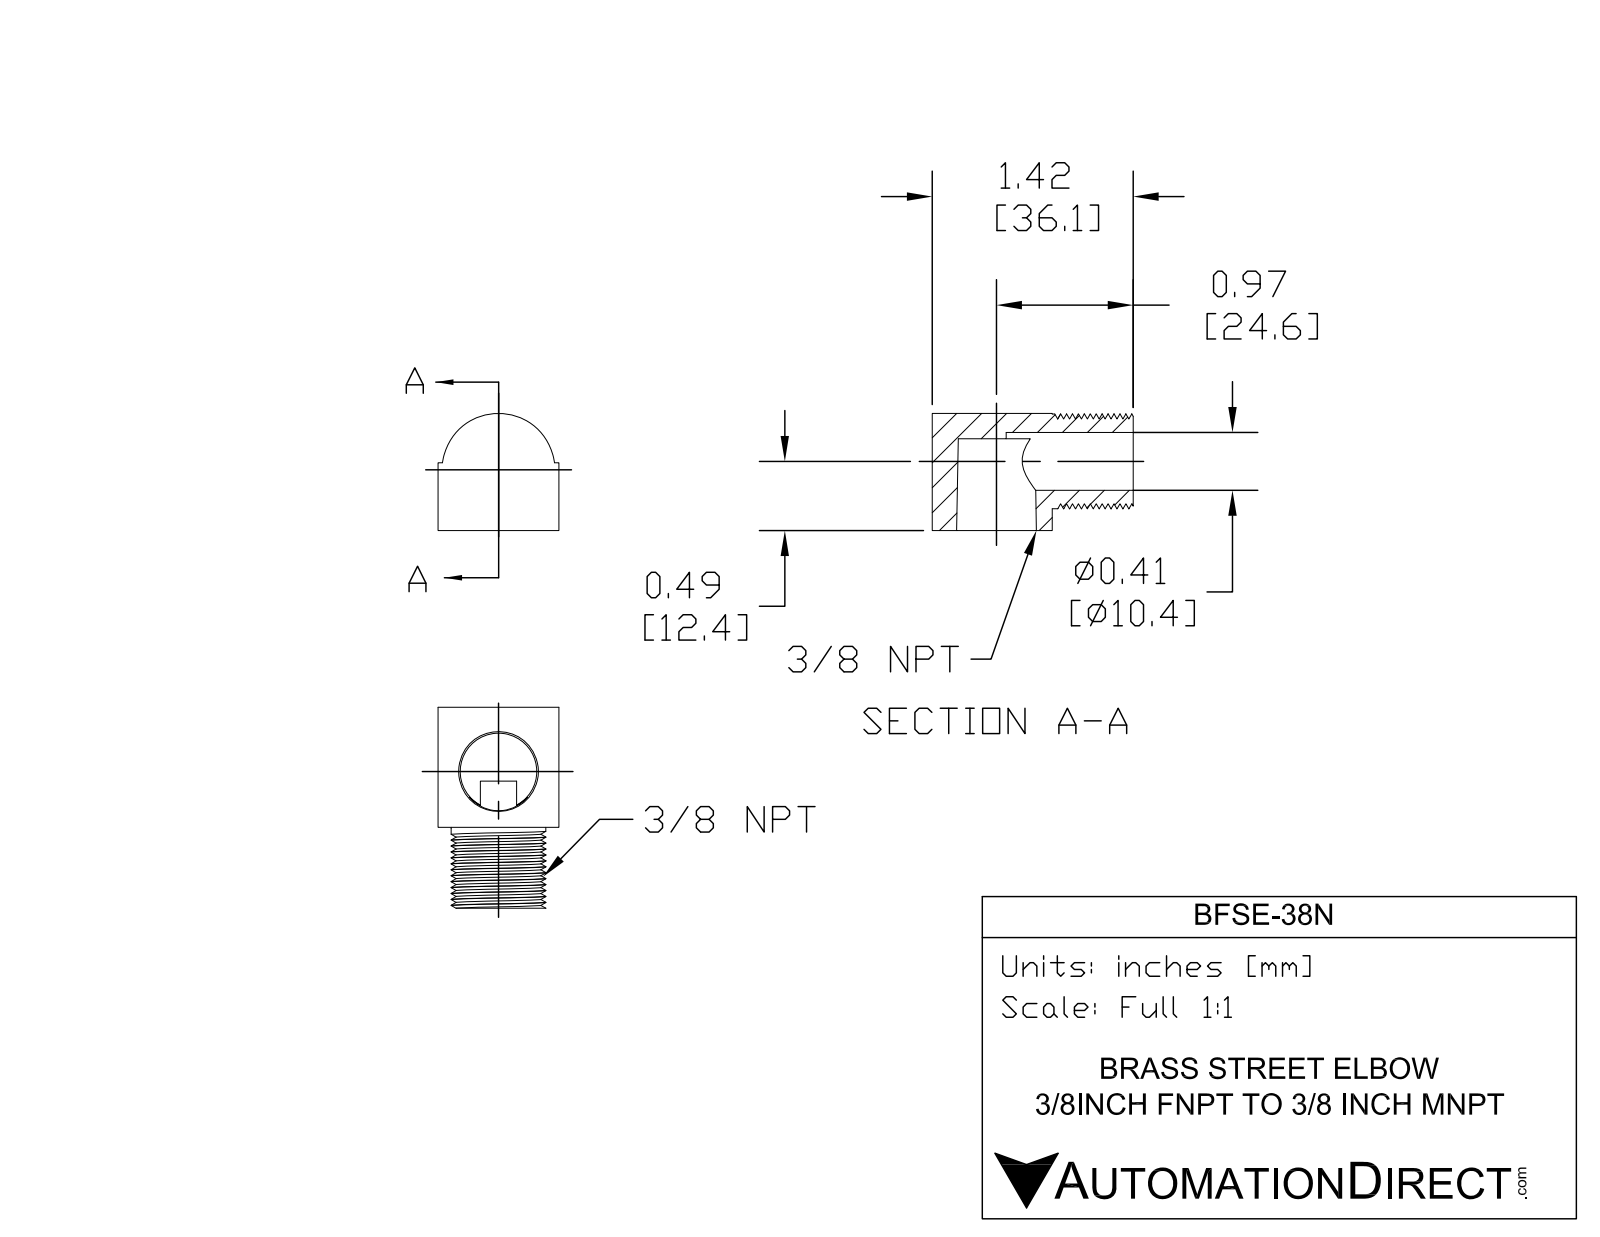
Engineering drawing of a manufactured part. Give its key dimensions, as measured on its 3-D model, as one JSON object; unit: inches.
{"part_name": "BFSE-38N", "step_written_by": "SolidWorks 2015 (CONFIG_CONTROL_DESIGN)", "units": "inches", "bodies": {"solids": 1, "faces": 45, "planar": 11, "cylindrical": 30, "other": 4}, "overall_size": [1.423, 0.856, 0.83], "volume_in3": 0.46, "surface_area_in2": 7.791, "round_holes": [[0.41, 1]], "round_bosses_or_shafts": [[0.67, 1]], "partial_cylinders_radius": [[0.4, 1]], "face_to_face_distances": [0.856, 0.85, 0.573, 1.423, 0.65, 0.48, 0.17, 0.9, 0.327, 0.523]}
